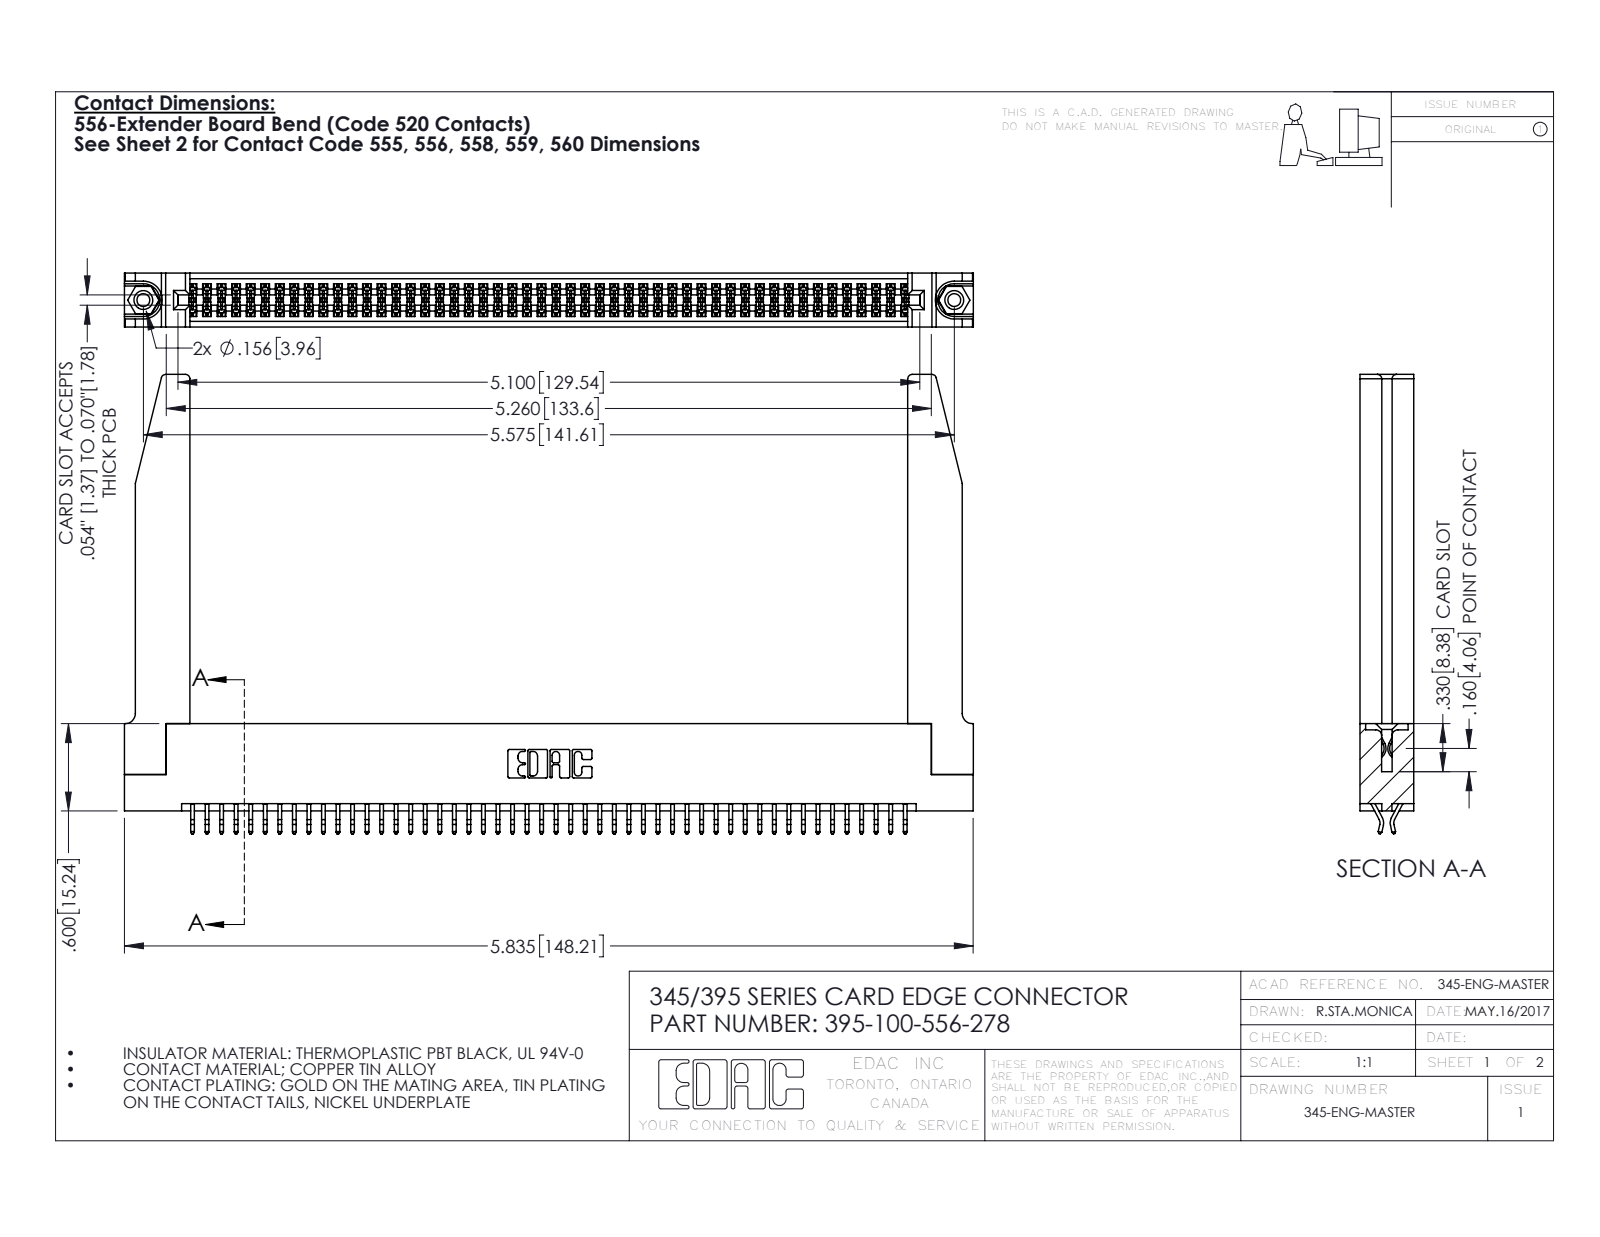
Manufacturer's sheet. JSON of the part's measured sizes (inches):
{"part_name": "395-100-556-278; 345-292-001_556 Tail; 345-250-001_345-250-001-102; 345 Part_Flush Mounting Lugs - 0.156 Dia-TH (+1 more)", "step_written_by": "SolidWorks 2016 (CONFIG_CONTROL_DESIGN)", "units": "inches", "bodies": {"solids": 105, "faces": 5960, "planar": 3922, "cylindrical": 1986, "other": 52}, "overall_size": [5.836, 3.157, 0.37], "volume_in3": 1.357, "surface_area_in2": 43.86, "round_holes": [[0.089, 2], [0.125, 2], [0.156, 2], [0.064, 1]], "round_bosses_or_shafts": [[0.155, 2]], "partial_cylinders_radius": [[0.006, 150], [0.01, 22], [0.03, 8], [0.007, 6], [0.031, 6], [0.026, 3], [0.01, 2], [0.014, 2]], "face_to_face_distances": [0.072, 0.37, 0.298, 0.2, 0.025, 0.098, 0.272, 0.225, 0.175, 0.15], "hole_center_spacings": [0.27, 5.339, 5.575]}
